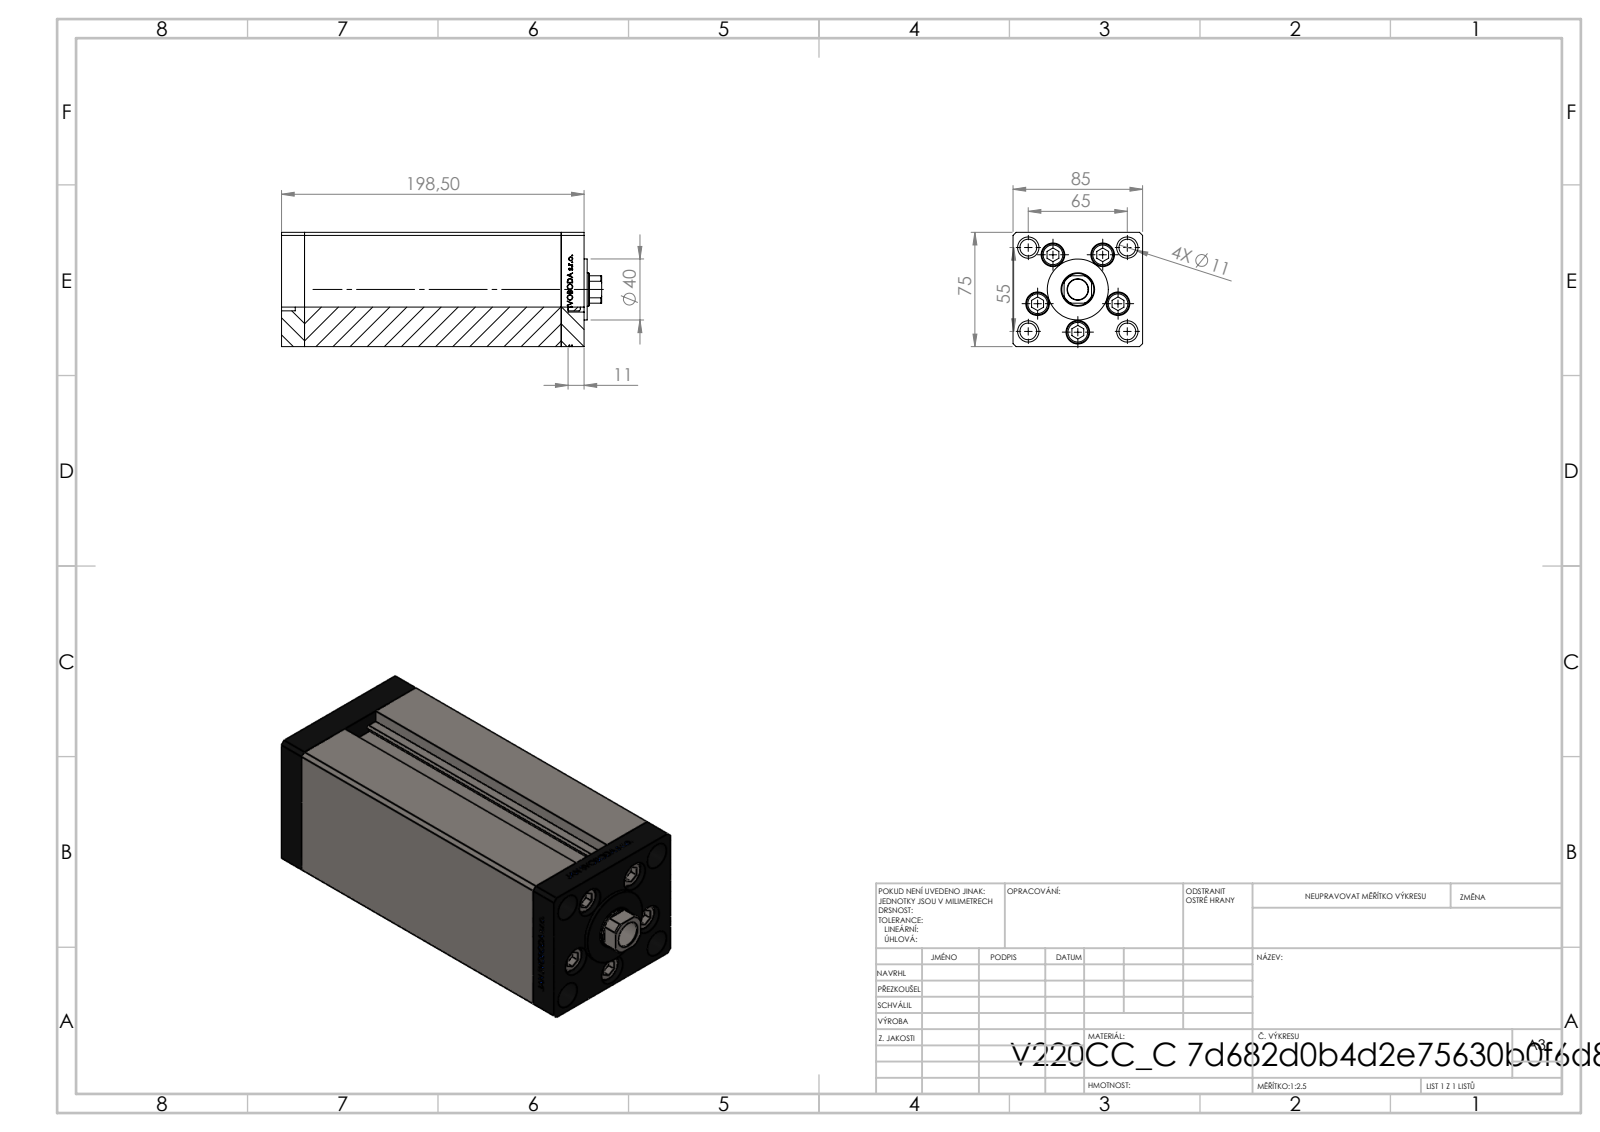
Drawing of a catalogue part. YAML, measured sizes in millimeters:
part_name: "V220C BACK_C; V220C_C MIDDLE; V220C FRONT; V220C_VC_C (+1 more)"
step_written_by: "SolidWorks 2019 (CONFIG_CONTROL_DESIGN)"
units: millimeters
bodies: {solids: 13, faces: 1163, planar: 542, cylindrical: 159, other: 462}
overall_size: [210, 85, 75]
volume: 1049000
surface_area: 192844
round_holes:
  - {diameter: 11, count: 9}
  - {diameter: 15.5, count: 5}
  - {diameter: 10, count: 4}
  - {diameter: 14, count: 4}
  - {diameter: 13.5, count: 1}
  - {diameter: 14.5, count: 1}
  - {diameter: 22, count: 1}
round_bosses_or_shafts:
  - {diameter: 8, count: 5}
  - {diameter: 14.5, count: 4}
  - {diameter: 40, count: 1}
partial_cylinders:
  - {radius: 0.93, count: 2}
  - {radius: 10.5, count: 1}
face_to_face_distances: [85, 75, 168.5, 15, 183.5, 10.5, 198.5, 34.25, 68.5, 164.25]
hole_center_spacings: [28, 42.57, 16.86, 19.17, 32.33, 32.5, 33.63, 37.33]
